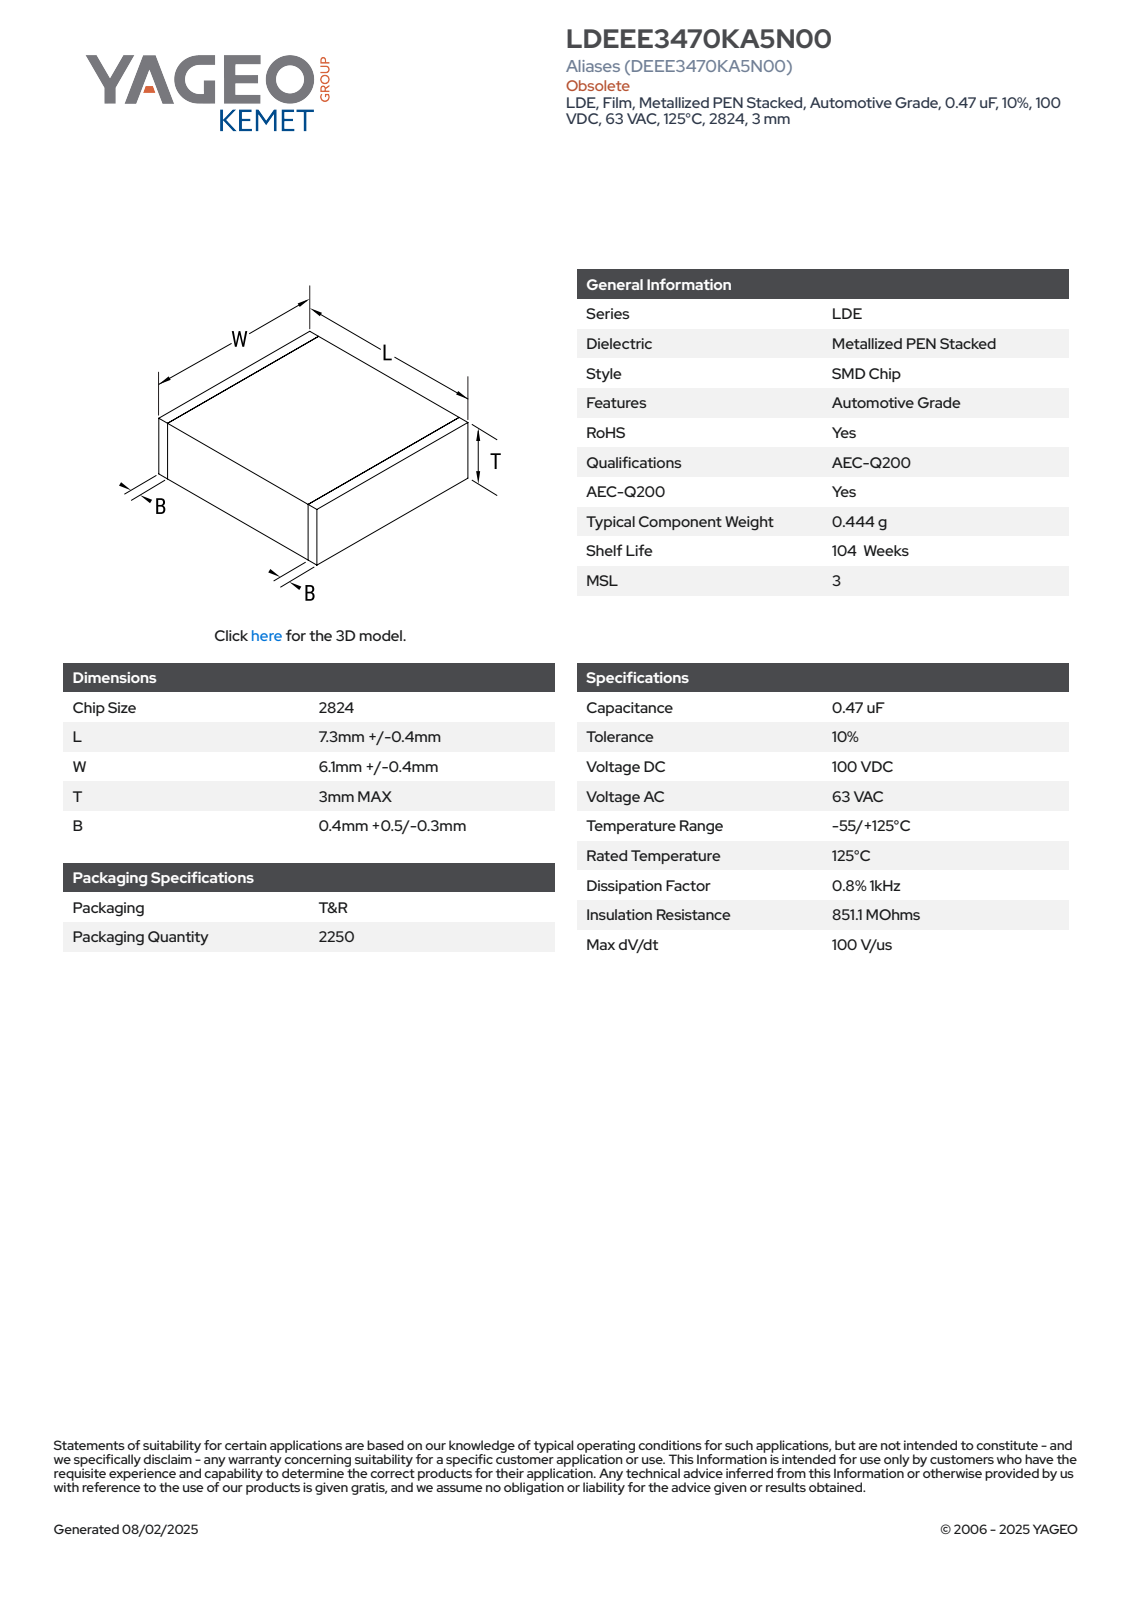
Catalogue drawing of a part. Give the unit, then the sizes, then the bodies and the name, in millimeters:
Units: millimetres
Overall size (bounding box): 7.7 × 6.5 × 3
Main face-to-face distances: 2.98, 6.48, 7.7, 2.99, 3, 6.49, 6.5, 0.5, 7.2, 6.7
Volume: 149 mm³ · Surface area: 188 mm²
Bodies: 4 solids, 73 faces (73 planar, 0 cylindrical, 0 other)
Part name (STEP PRODUCT): CFS_LDELDB_2824_L7.7W6.5T3B0.9
STEP written by: SolidWorks 2020 (AUTOMOTIVE_DESIGN)
